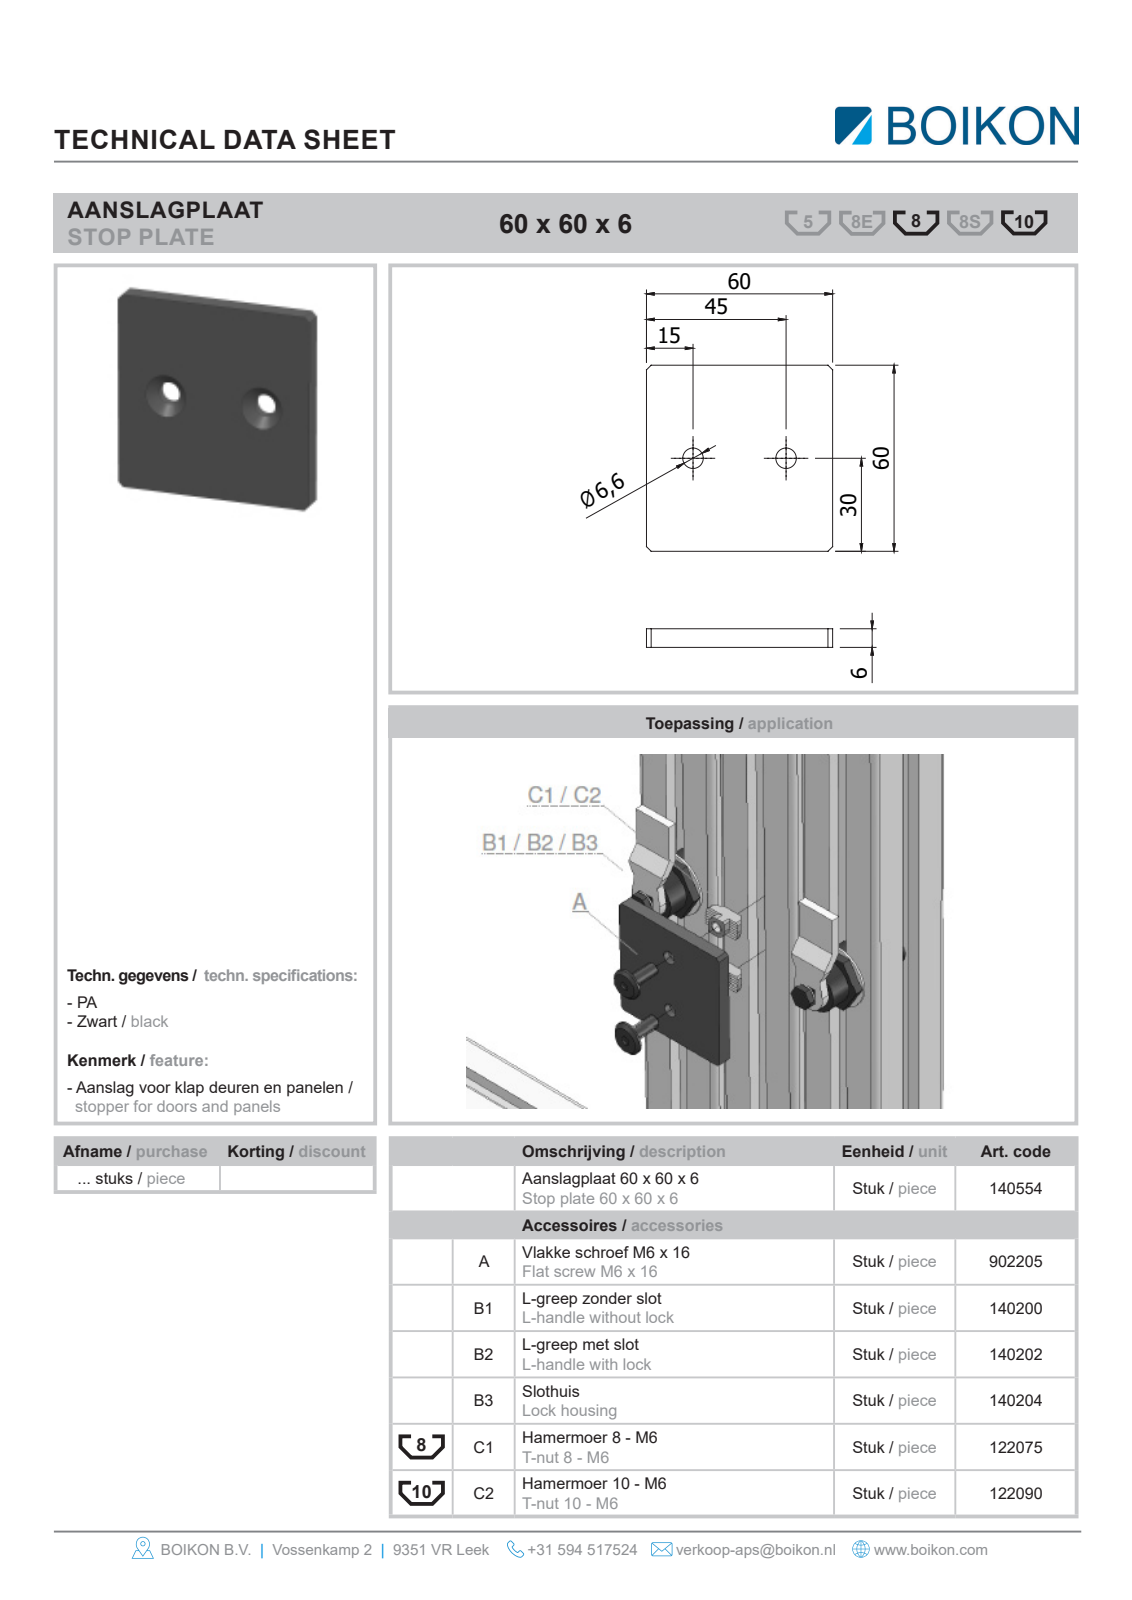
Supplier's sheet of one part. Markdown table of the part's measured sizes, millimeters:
| quantity | value |
| --- | --- |
| part name | Root; 140554Tegenhoudplaatje 60x60x6BOIKON |
| STEP written by | HiCAD 2013 1802.4 Build 509 (AUTOMOTIVE_DESIGN) |
| units | millimeters |
| bodies | 1 solid, 14 faces (10 planar, 2 cylindrical, 2 other) |
| overall size | 60 × 60 × 6.3 |
| volume | 20 919 mm³ |
| surface area | 8 672 mm² |
| round holes (diameter × count) | 6.6 × 2 |
| main face-to-face distances | 6, 60, 82.72 |
| hole center spacings | 30 |
